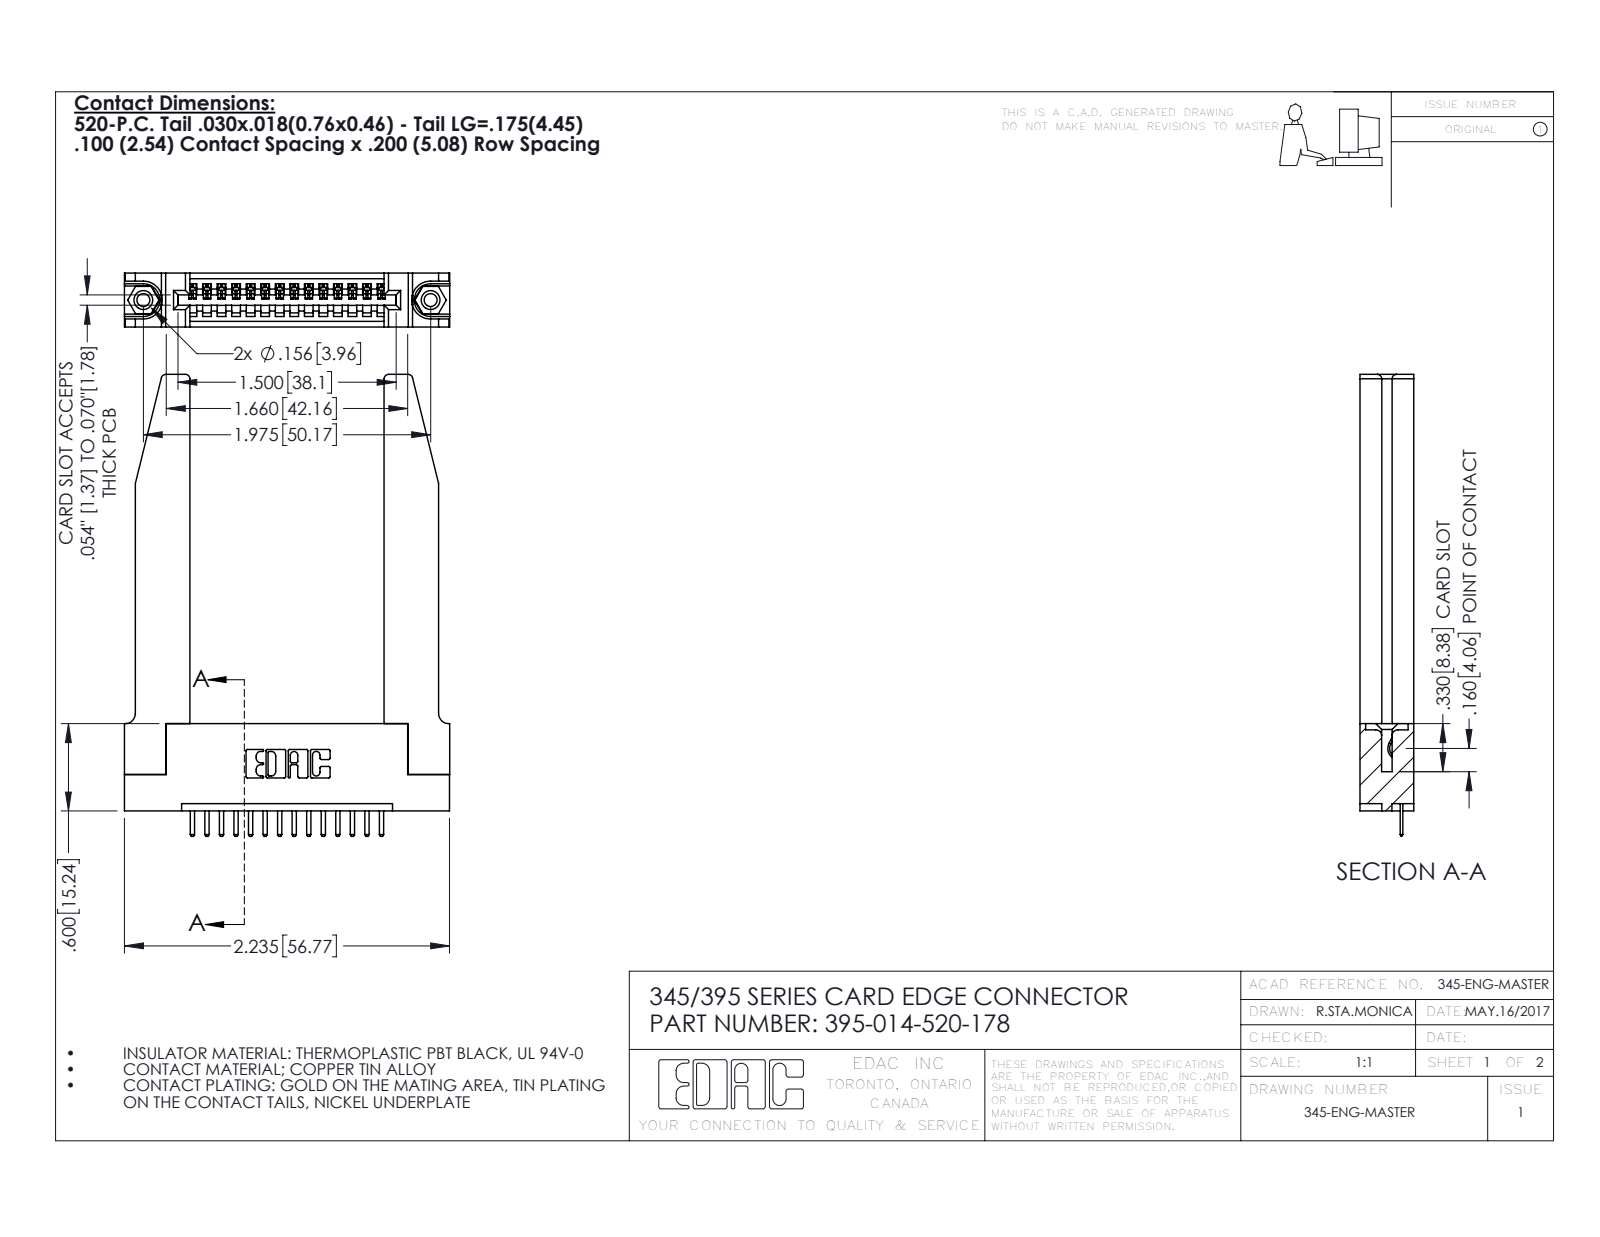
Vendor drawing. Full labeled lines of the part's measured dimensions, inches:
Part name (STEP PRODUCT): 395-014-520-178; 345-292-001_345-293-120; 345-250-001_345-250-001-102; 345-220-078_345-220-078 (+1 more)
STEP written by: SolidWorks 2016 (CONFIG_CONTROL_DESIGN)
Units: inches
Bodies: 19 solids, 1228 faces (810 planar, 366 cylindrical, 52 other)
Overall size (bounding box): 3.175 × 2.236 × 0.37
Volume: 0.787 in³ · Surface area: 20.37 in²
Round holes (diameter × count): ⌀0.089 ×2, ⌀0.125 ×2, ⌀0.156 ×2, ⌀0.064 ×1
Round bosses / shafts (diameter × count): ⌀0.155 ×2
Partial cylindrical surfaces — rounded edges, fillets, slot ends (radius × count): R0.01 ×30, R0.006 ×28, R0.01 ×22, R0.03 ×8, R0.007 ×6, R0.031 ×6, R0.026 ×3, R0.031 ×2
Main face-to-face distances: 0.37, 0.072, 0.298, 0.2, 0.148, 0.15, 0.077, 0.22, 1.335, 0.098
Hole centre spacings: 0.27, 1.742, 1.975
